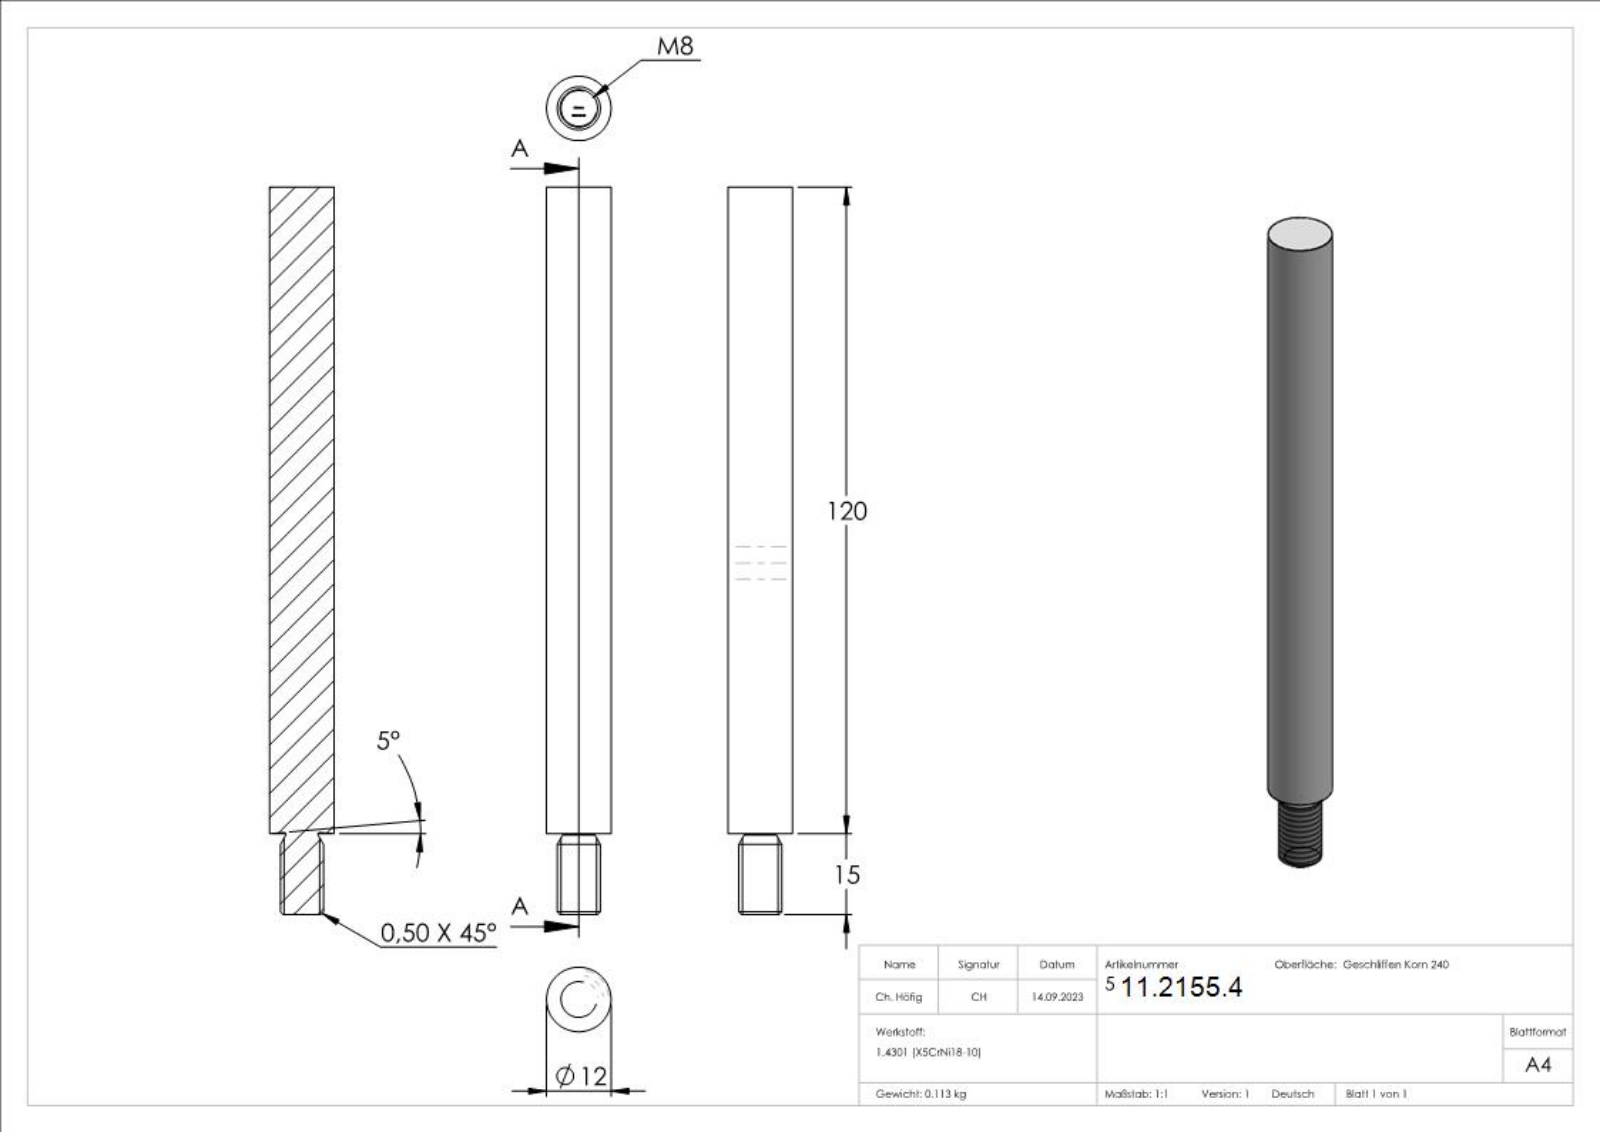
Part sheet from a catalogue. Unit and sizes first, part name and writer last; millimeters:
Units: millimetres
Overall size (bounding box): 135 × 12 × 12
Round bosses / shafts (diameter × count): ⌀12 ×1, ⌀8 ×1
Main face-to-face distances: 135, 134.9, 0.59, 1.44, 0.31, 1.33, 0.33, 1.24, 1.53, 0.61
Volume: 14 287 mm³ · Surface area: 5 145 mm²
Bodies: 1 solid, 255 faces (123 planar, 2 cylindrical, 130 other)
Part name (STEP PRODUCT): 50236-240-120
STEP written by: SolidWorks 2018 (CONFIG_CONTROL_DESIGN)
